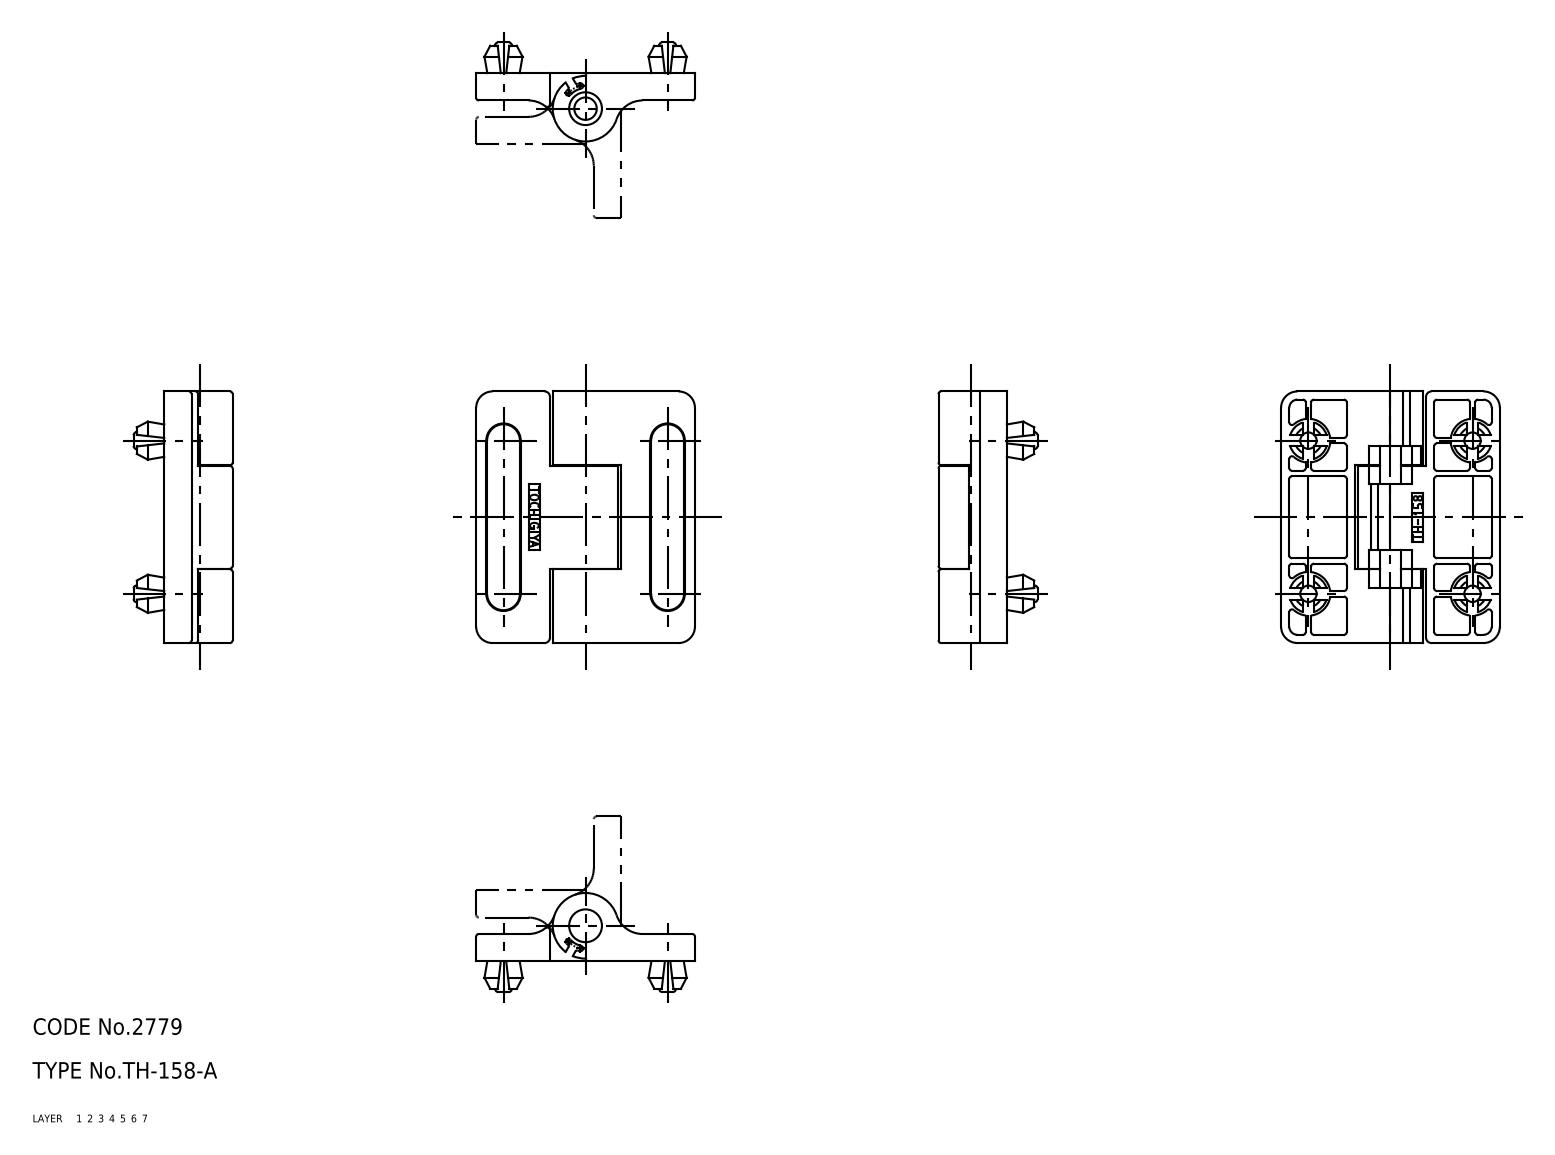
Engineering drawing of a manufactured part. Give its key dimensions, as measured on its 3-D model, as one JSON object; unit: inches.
{"part_name": "67128855; 67128868; 67128881; 67128894 (+1 more)", "step_written_by": "CADfix (AUTOMOTIVE_DESIGN)", "units": "inches", "bodies": {"solids": 5, "faces": 422, "planar": 0, "cylindrical": 0, "other": 422}, "overall_size": [1.811, 1.575, 0.713], "volume_in3": 0.629, "surface_area_in2": 15.72}
